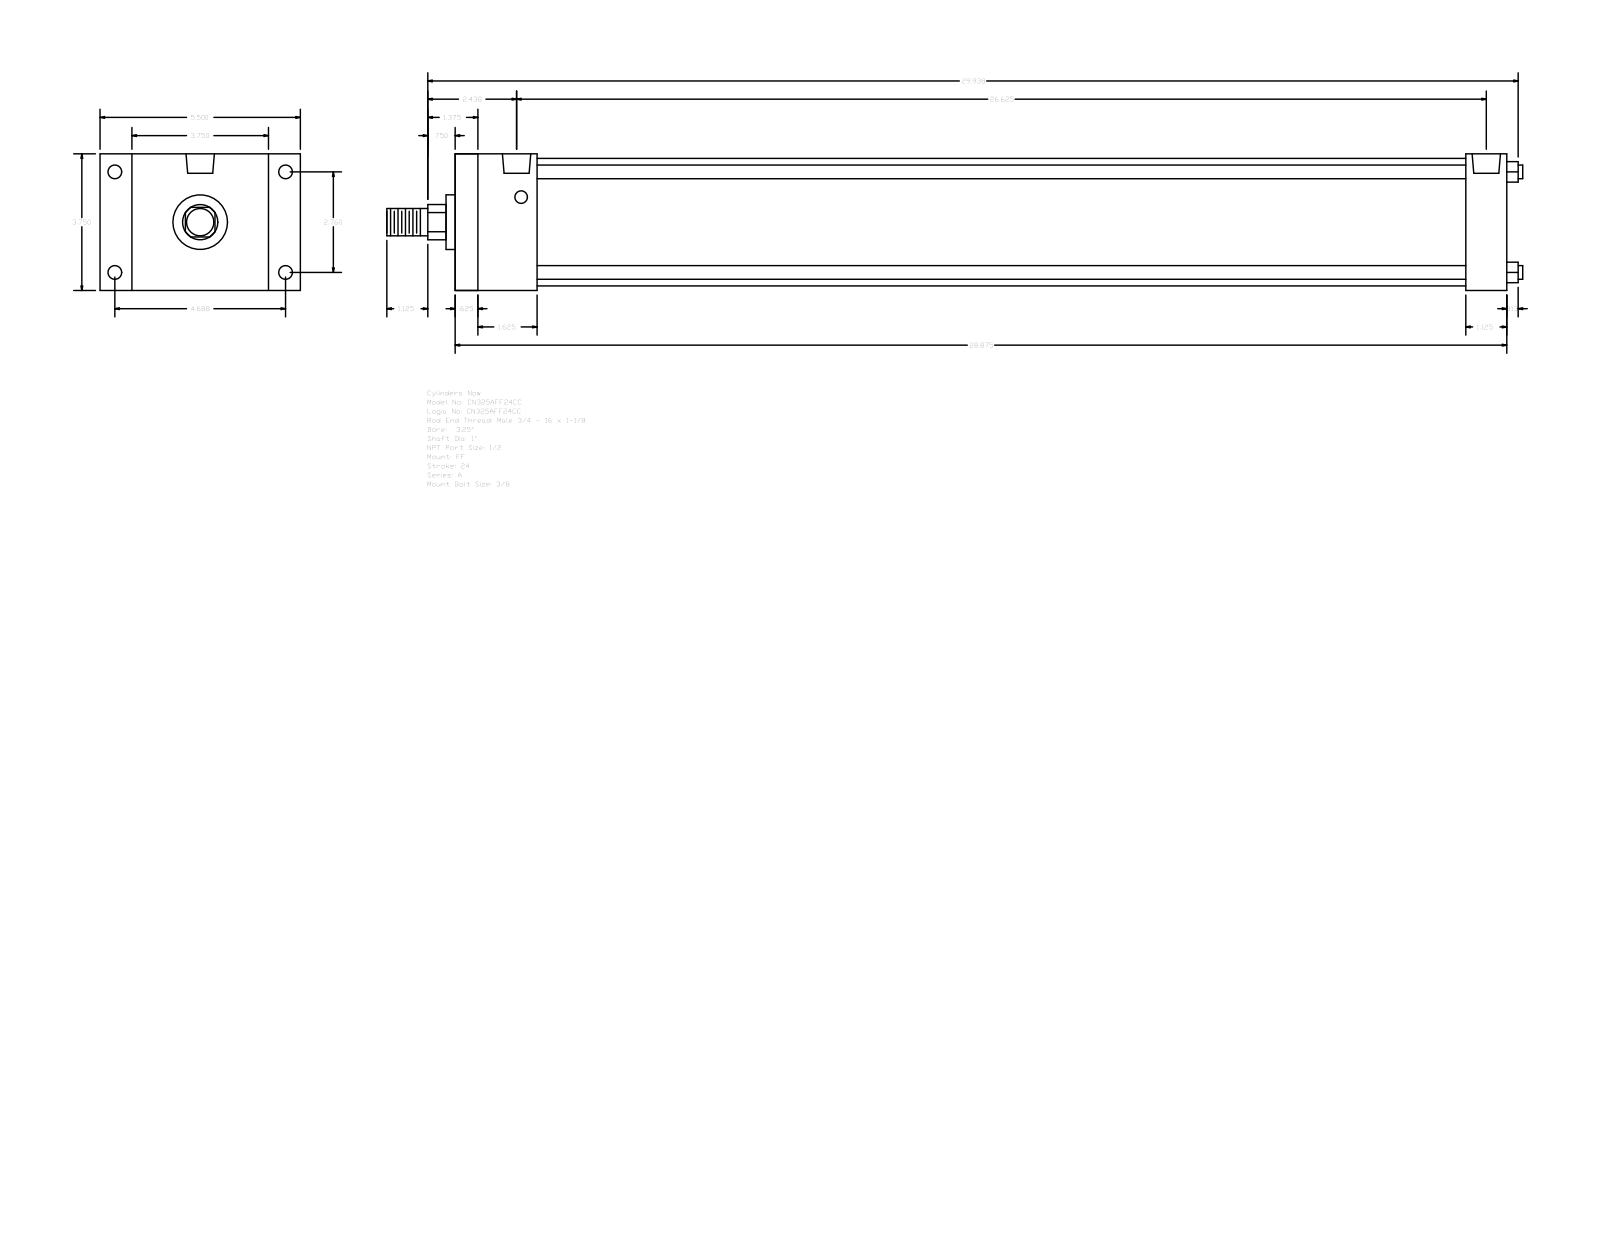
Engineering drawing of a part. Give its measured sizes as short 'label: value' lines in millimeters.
name: A_FF__0325_1
written by: GSSL Pune (CONFIG_CONTROL_DESIGN)
unit: mm
bodies: 0 solids, 92 faces (64 planar, 28 cylindrical, 0 other)
size: 792.16 × 139.7 × 95.25
holes: 4× ⌀8.73, 4× ⌀9.53, 2× ⌀19.77
bosses: 4× ⌀9.53, 1× ⌀88.9, 1× ⌀38.1, 1× ⌀25.4, 1× ⌀19.05
rounds: 1× R12.29
face distances: 95.24, 733.43, 15.87, 717.56, 22.23, 117.47, 57.15, 704.85, 41.28, 688.98
hole spacings: 3.18, 70.1, 119.06, 138.16, 669.92, 673.1, 676.28
